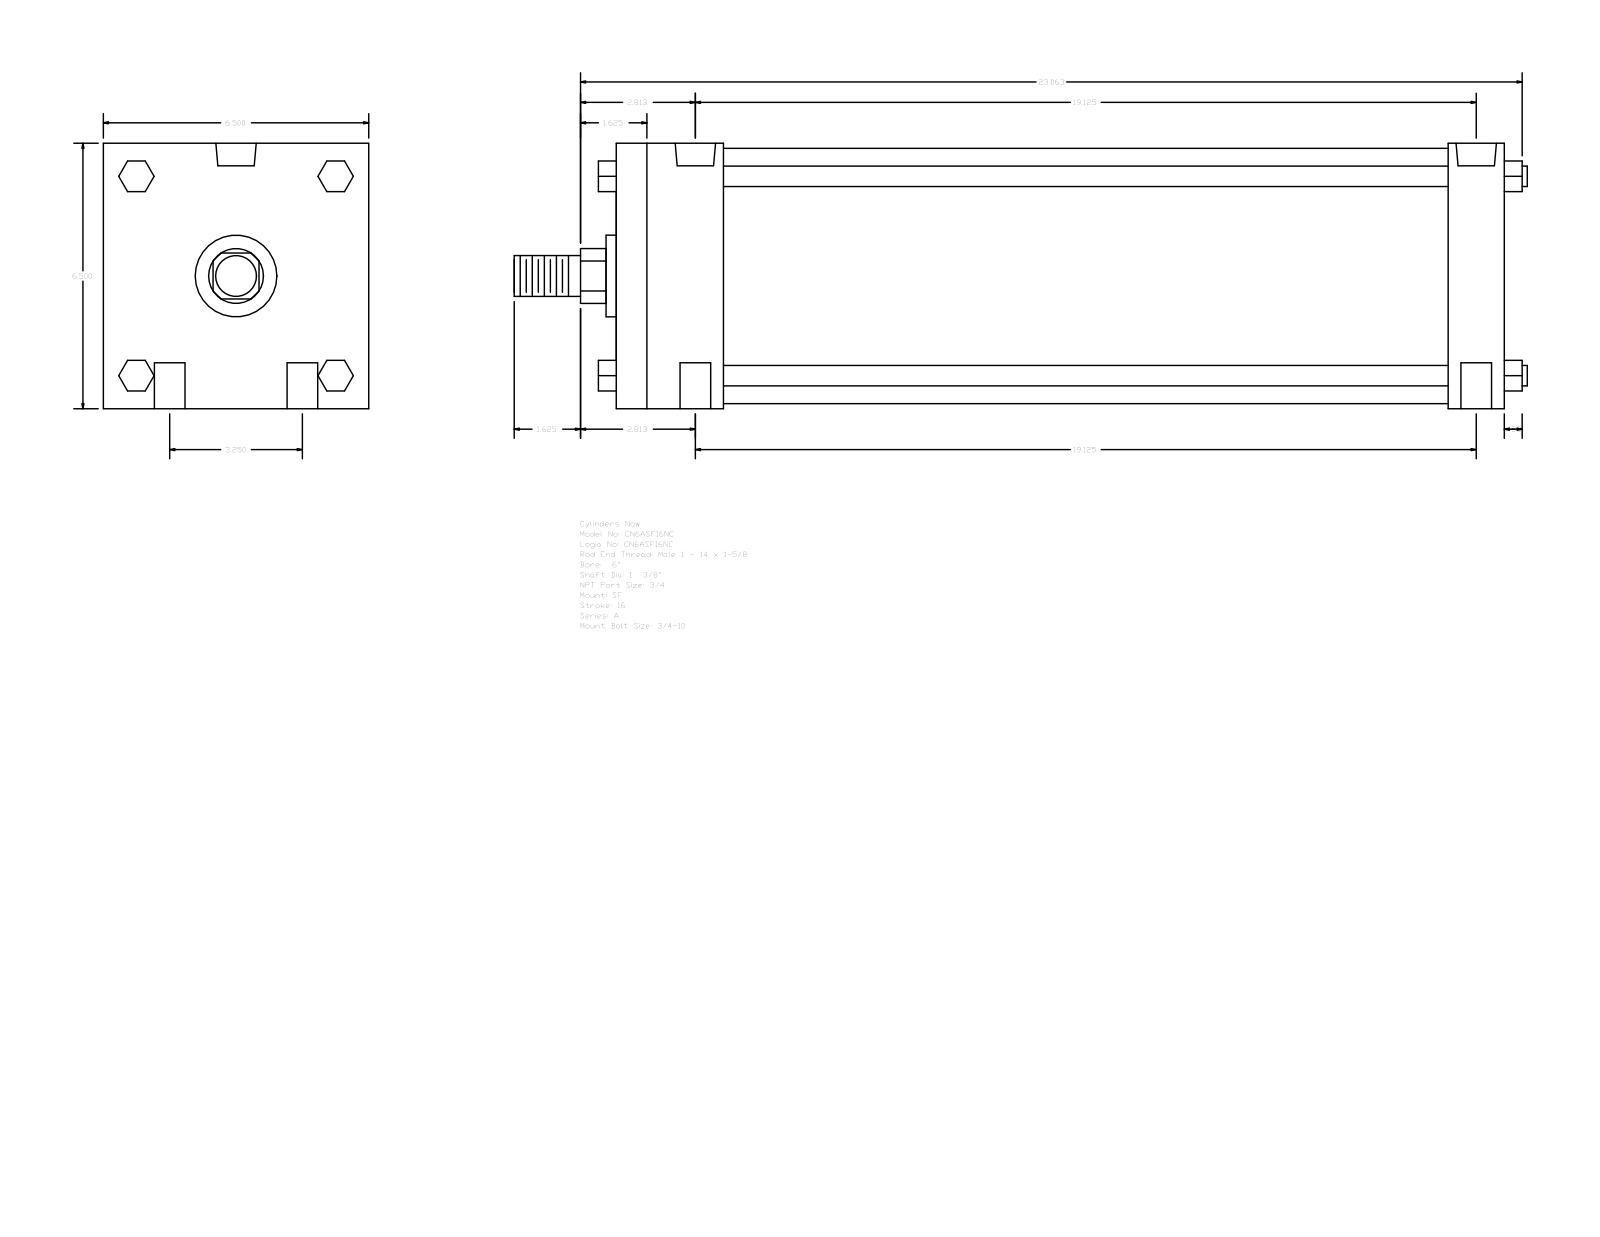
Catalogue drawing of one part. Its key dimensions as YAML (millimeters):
part_name: "A_SF__0600_1.375"
step_written_by: "GSSL Pune (CONFIG_CONTROL_DESIGN)"
units: millimeters
bodies: {solids: 0, faces: 124, planar: 94, cylindrical: 30, other: 0}
overall_size: [630.24, 165.1, 165.1]
round_holes:
  - {diameter: 19.05, count: 4}
  - {diameter: 15.08, count: 2}
  - {diameter: 25.12, count: 2}
round_bosses_or_shafts:
  - {diameter: 12.7, count: 4}
  - {diameter: 158.75, count: 1}
  - {diameter: 50.8, count: 1}
  - {diameter: 34.92, count: 1}
  - {diameter: 25.4, count: 1}
partial_cylinders:
  - {radius: 17.06, count: 1}
face_to_face_distances: [165.1, 552.44, 517.52, 34.92, 66.67, 450.85, 485.77, 19.05, 61.97, 107.34]
hole_center_spacings: [41.27, 487.52, 485.77, 82.54, 492.73, 474.65]
